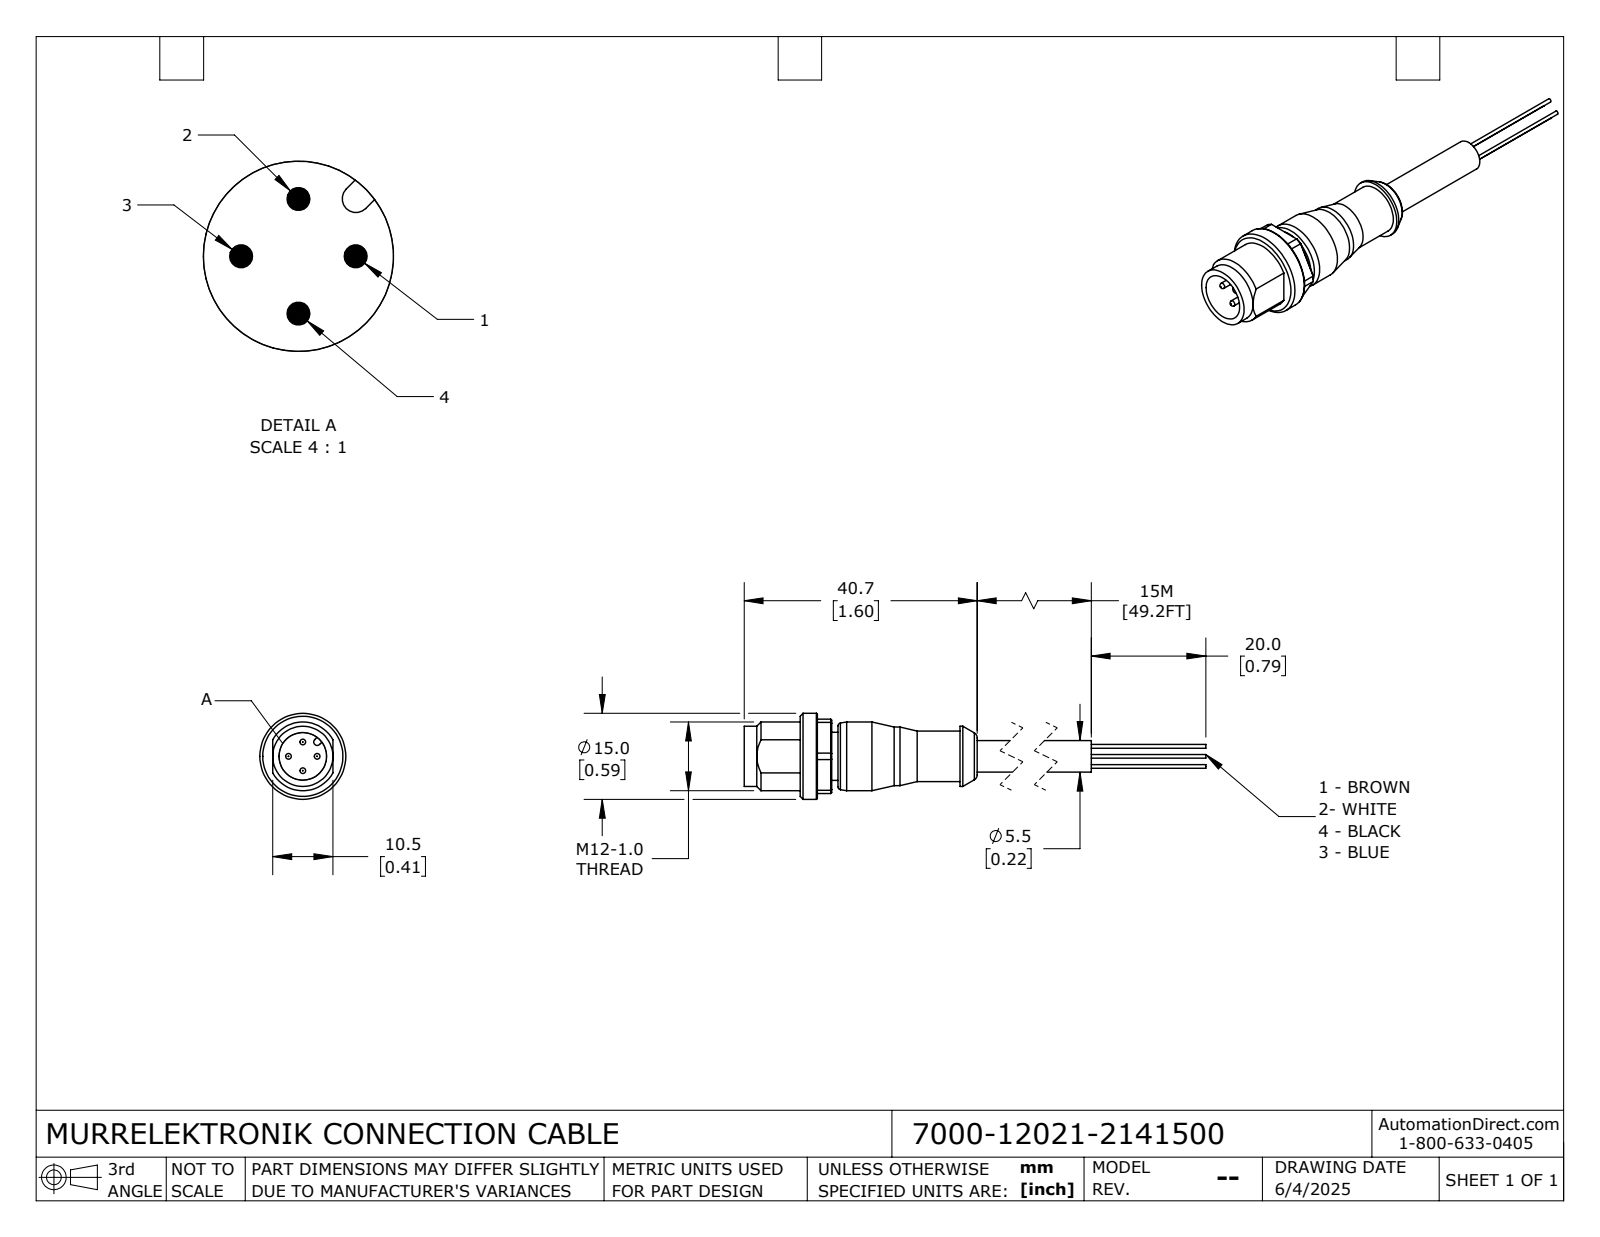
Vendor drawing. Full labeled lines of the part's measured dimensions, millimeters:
Part name (STEP PRODUCT): 7000-12021-2141500
STEP written by: SolidWorks 2024 (CONFIG_CONTROL_DESIGN)
Units: millimetres
Bodies: 1 solid, 110 faces (34 planar, 43 cylindrical, 33 other)
Overall size (bounding box): 80.7 × 15 × 15
Volume: 3 989 mm³ · Surface area: 2 637 mm²
Round holes (diameter × count): ⌀8.3 ×1
Round bosses / shafts (diameter × count): ⌀1 ×4, ⌀0.64 ×4, ⌀15 ×1, ⌀12 ×1, ⌀10.5 ×1, ⌀10.2 ×1, ⌀8.8 ×1, ⌀8.4 ×1
Partial cylindrical surfaces — rounded edges, fillets, slot ends (radius × count): R0.6 ×1, R7.2 ×1
Main face-to-face distances: 6.4, 0.9, 5.5, 13, 10.5, 27.9, 7.5, 6.6, 1.1, 8.9
